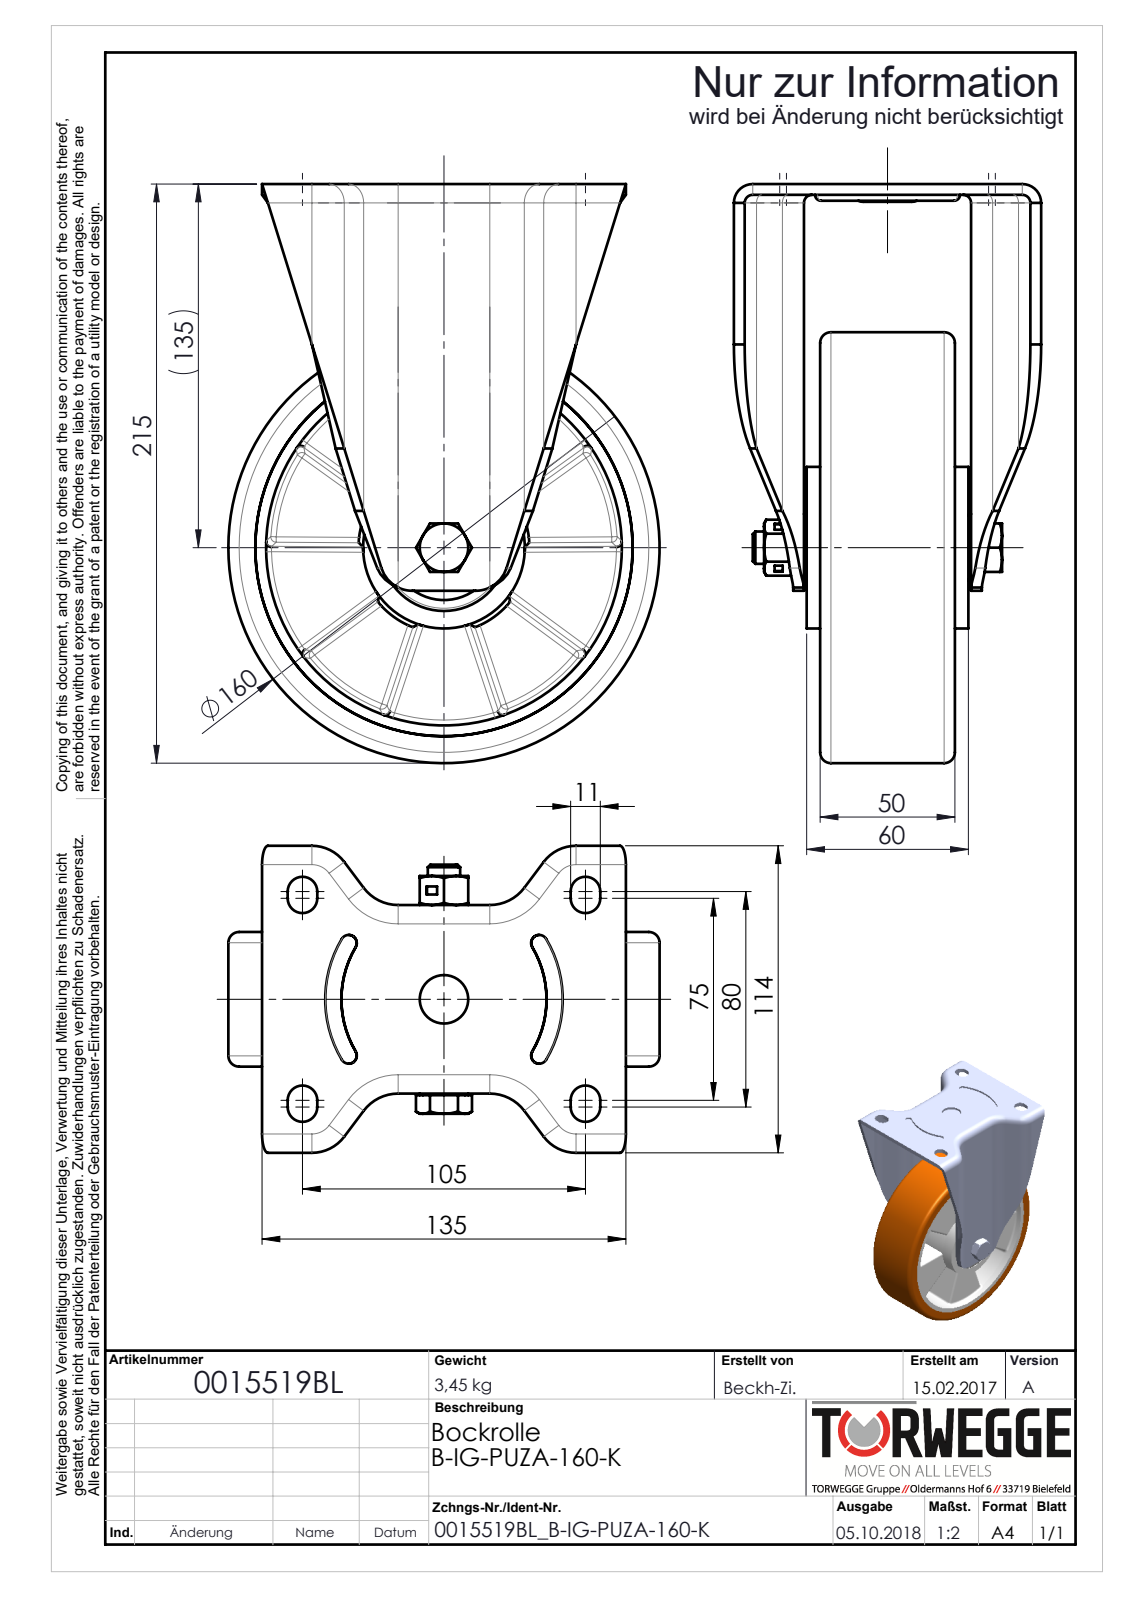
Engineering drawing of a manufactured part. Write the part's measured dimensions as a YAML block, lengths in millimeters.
part_name: "0015519BL_B-IG-PUZA-160-K"
step_written_by: "SolidWorks 2016 (AUTOMOTIVE_DESIGN)"
units: millimeters
bodies: {solids: 7, faces: 522, planar: 138, cylindrical: 146, other: 238}
overall_size: [215, 160, 114]
volume: 758044
surface_area: 253704
round_holes:
  - {diameter: 10.2, count: 1}
  - {diameter: 12, count: 1}
  - {diameter: 12.2, count: 1}
  - {diameter: 12.5, count: 1}
  - {diameter: 18, count: 1}
  - {diameter: 20, count: 1}
  - {diameter: 132, count: 1}
  - {diameter: 140, count: 1}
round_bosses_or_shafts:
  - {diameter: 160, count: 1}
  - {diameter: 60, count: 1}
  - {diameter: 25, count: 1}
  - {diameter: 19.9, count: 1}
  - {diameter: 18, count: 1}
partial_cylinders:
  - {radius: 2, count: 40}
  - {radius: 3, count: 12}
  - {radius: 5.5, count: 8}
  - {radius: 7, count: 8}
  - {radius: 2.2, count: 4}
  - {radius: 11, count: 4}
  - {radius: 15, count: 4}
  - {radius: 16, count: 4}
face_to_face_distances: [4, 16.5, 49.5, 60, 6, 5, 66, 12.5, 53.5, 56]
